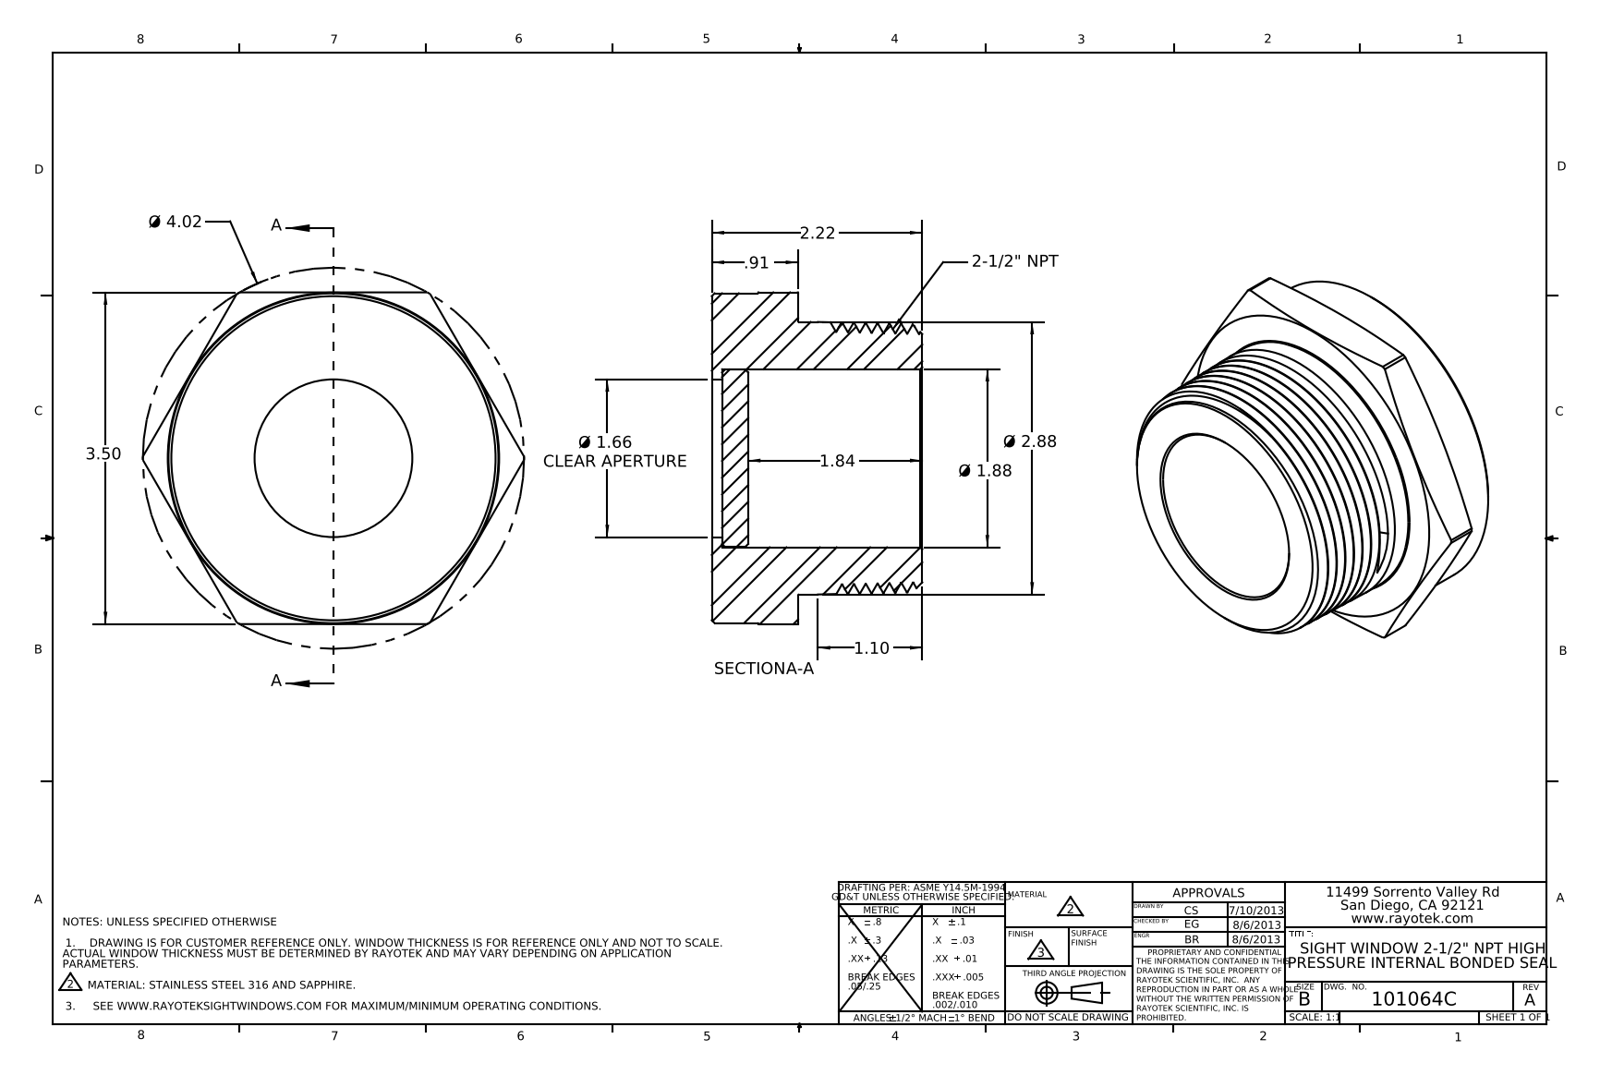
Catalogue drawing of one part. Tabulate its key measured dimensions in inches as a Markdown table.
| quantity | value |
| --- | --- |
| part name | 101064; 402064; 403064 |
| STEP written by | SolidWorks 2012 (AUTOMOTIVE_DESIGN) |
| units | inches |
| bodies | 2 solids, 71 faces (15 planar, 17 cylindrical, 39 other) |
| overall size | 4.021 × 3.5 × 2.22 |
| volume | 11.68 in³ |
| surface area | 63.92 in² |
| round holes (diameter × count) | 1.664 × 1, 1.88 × 1 |
| round bosses / shafts (diameter × count) | 3.48 × 1, 2.875 × 1, 1.87 × 1 |
| partial cylindrical surfaces (radius × count) | 2.011 × 1 |
| main face-to-face distances | 0.108, 0.91, 0.802, 0.384, 0.276, 0.526, 2.22, 2.112, 1.836, 1.31 |
